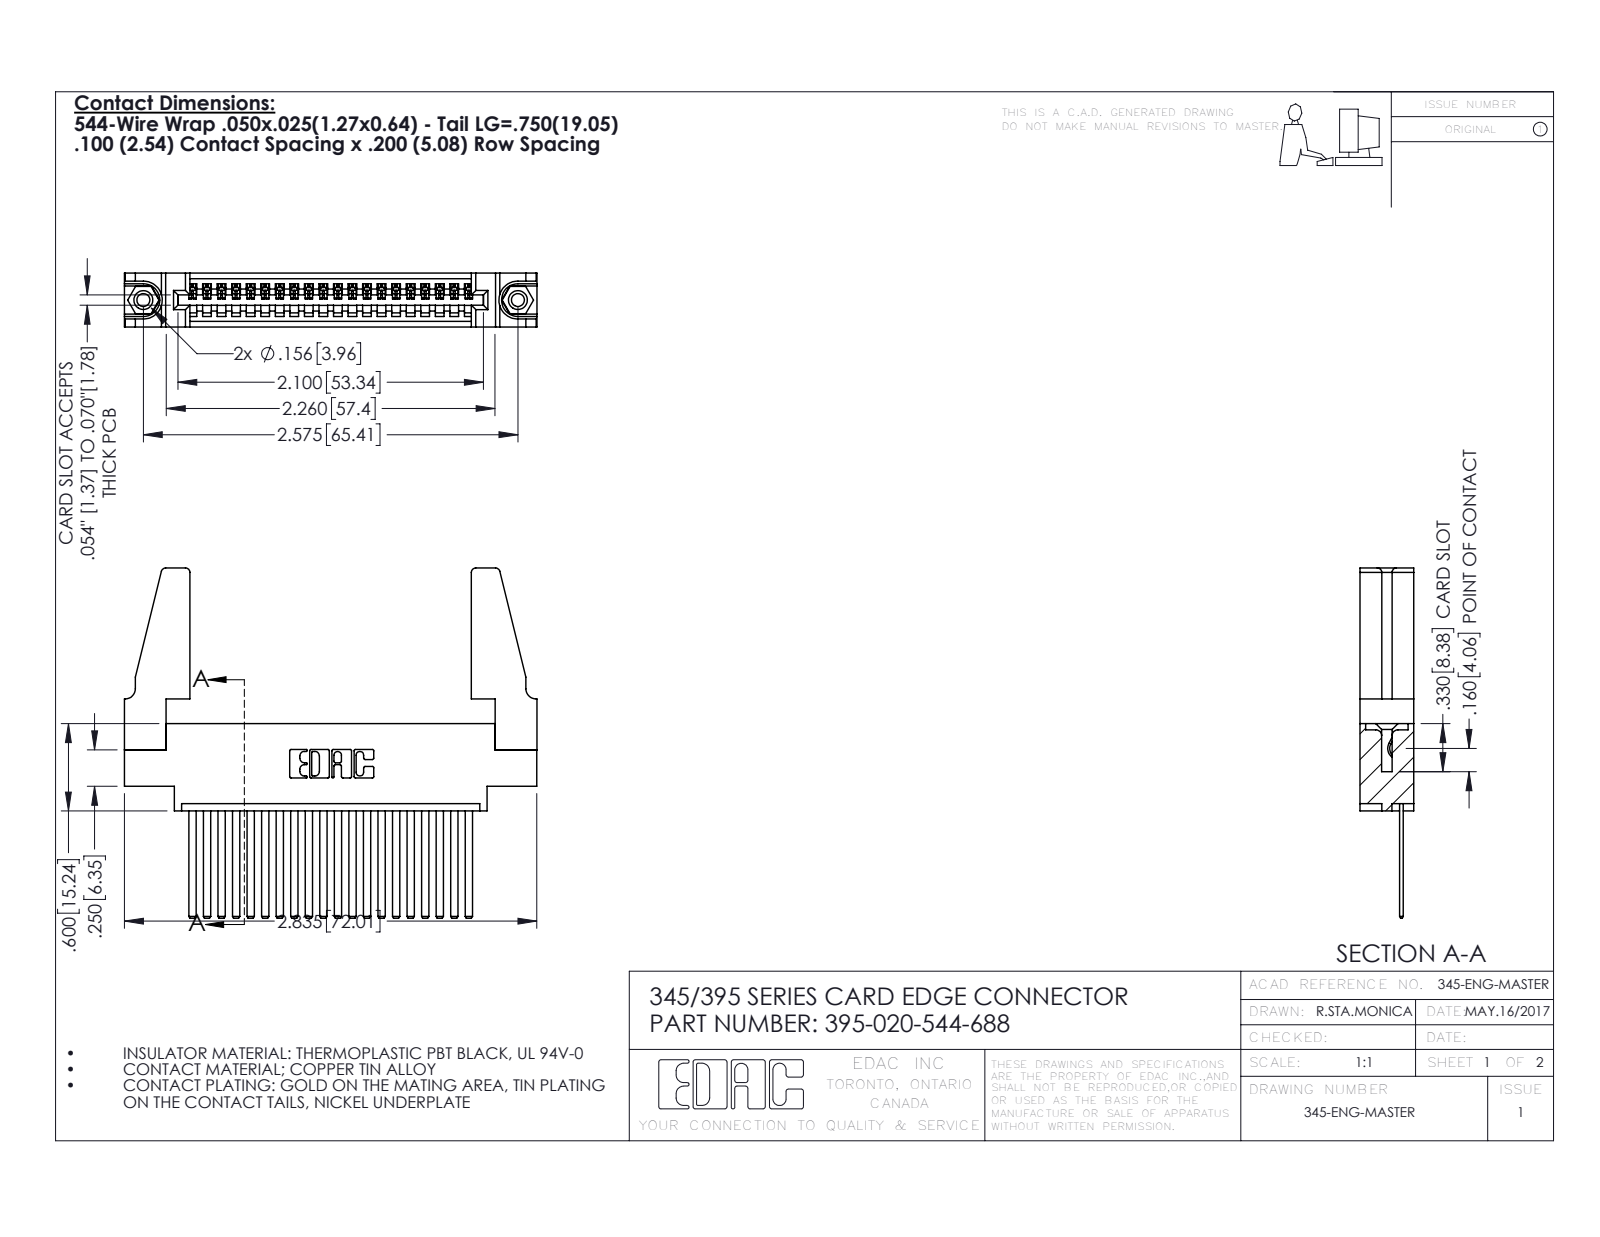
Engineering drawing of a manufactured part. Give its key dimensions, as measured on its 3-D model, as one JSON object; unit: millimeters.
{"part_name": "345 Part_0.170 Offset - 0.156 Dia-TH; 345-250-001_345-250-001-102; 395-020-544-688; 345-292-001_345-293-144 (+1 more)", "step_written_by": "SolidWorks 2016 (CONFIG_CONTROL_DESIGN)", "units": "millimeters", "bodies": {"solids": 25, "faces": 1294, "planar": 876, "cylindrical": 402, "other": 16}, "overall_size": [72, 61.1, 9.4], "volume_mm3": 10000, "surface_area_mm2": 12660, "round_holes": [[2.3, 2], [3.2, 2], [4, 2], [1.6, 1]], "round_bosses_or_shafts": [[3.9, 2]], "partial_cylinders_radius": [[0.2, 40], [0.3, 22], [0.8, 8], [0.2, 6], [0.8, 6], [0.7, 3], [0.8, 2], [1, 2]], "face_to_face_distances": [1.8, 9.4, 7.6, 2.5, 6.9, 0.6, 5.1, 5.7, 4.4, 3.8], "hole_center_spacings": [6.9, 59.5, 65.4]}
